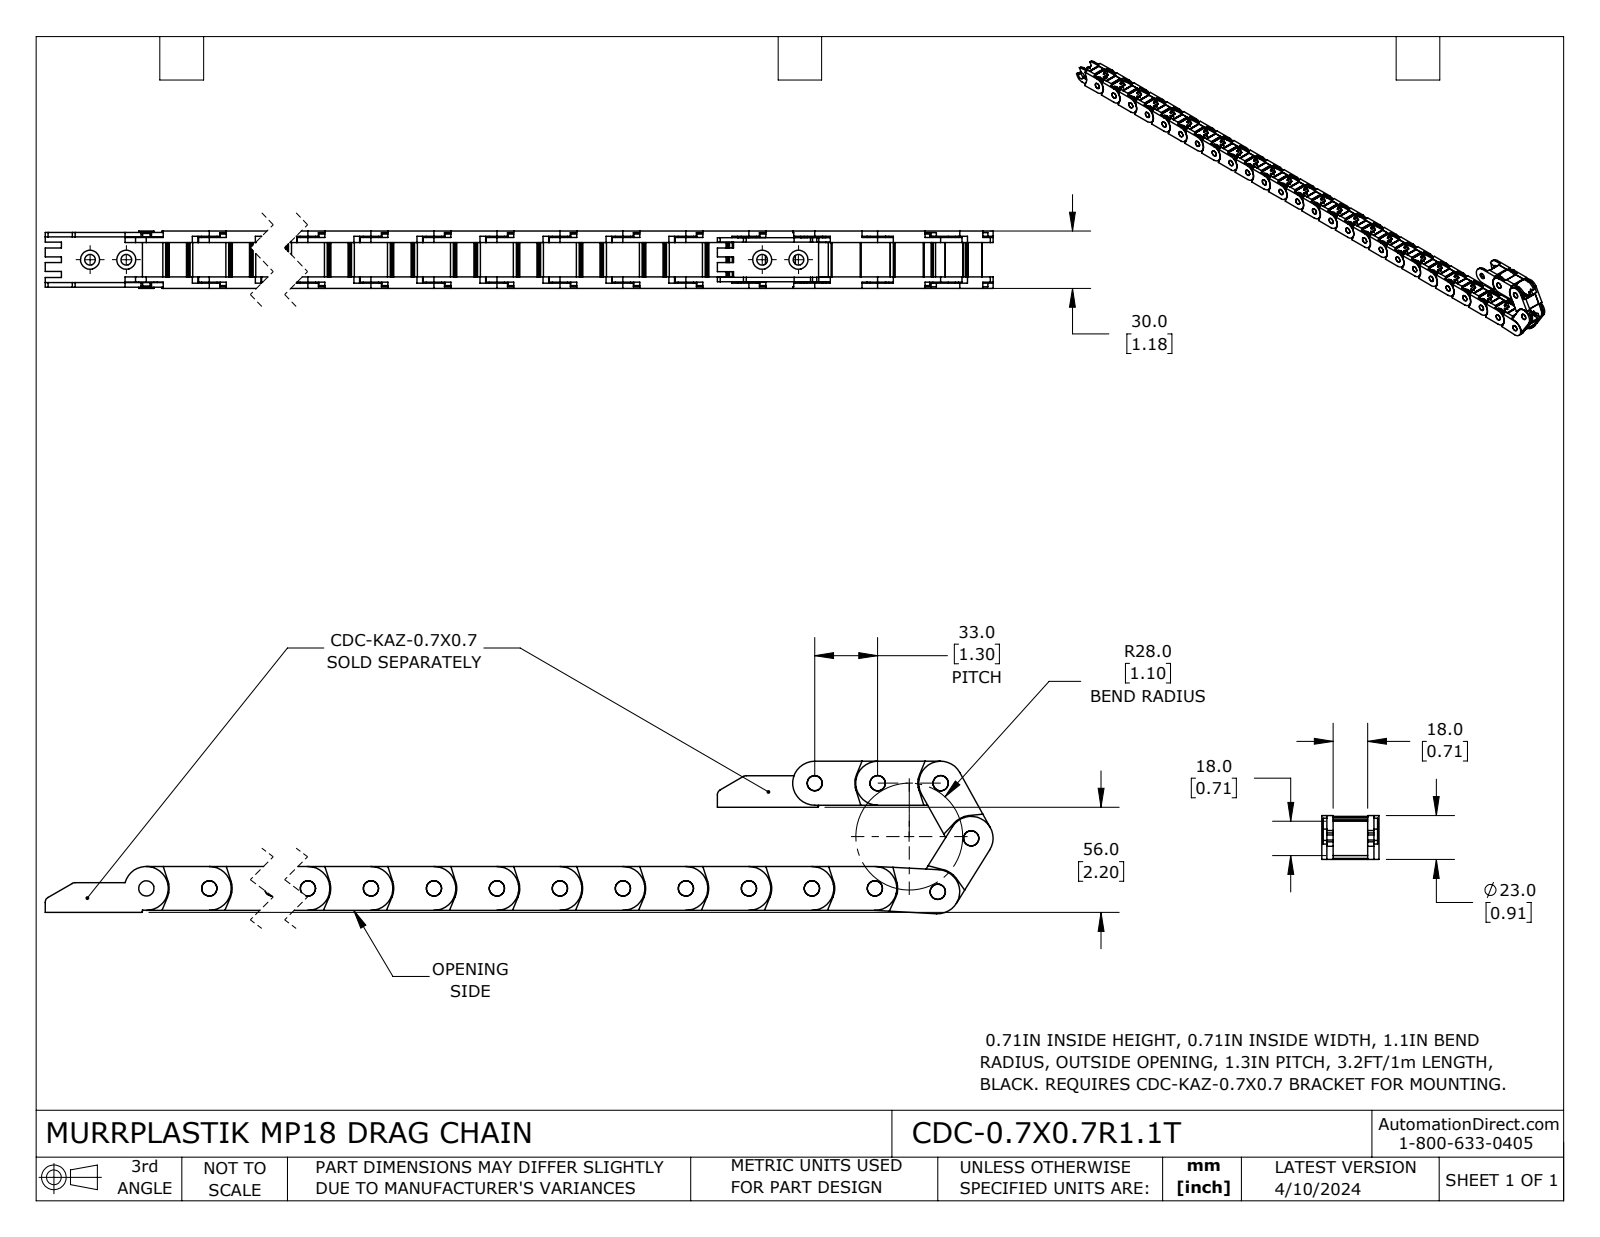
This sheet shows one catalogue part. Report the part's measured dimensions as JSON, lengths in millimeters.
{"part_name": "CDC-0.7X0.7R1.1T", "step_written_by": "SolidWorks 2023 (CONFIG_CONTROL_DESIGN)", "units": "millimeters", "bodies": {"solids": 30, "faces": 2730, "planar": 1530, "cylindrical": 1200, "other": 0}, "overall_size": [898.13, 79.84, 30], "volume_mm3": 264064, "surface_area_mm2": 207502, "round_holes": [[8, 30]], "round_bosses_or_shafts": [[8, 1]], "partial_cylinders_radius": [[0.5, 120], [1.5, 120], [0.2, 60], [0.3, 60], [11.5, 31], [11.95, 31], [5, 30], [5.45, 30]], "face_to_face_distances": [24, 6, 2.7, 3.3, 30, 26.7, 20.7, 18, 27.3, 0.6], "hole_center_spacings": [33, 66, 99, 132, 165, 198, 231, 264]}
